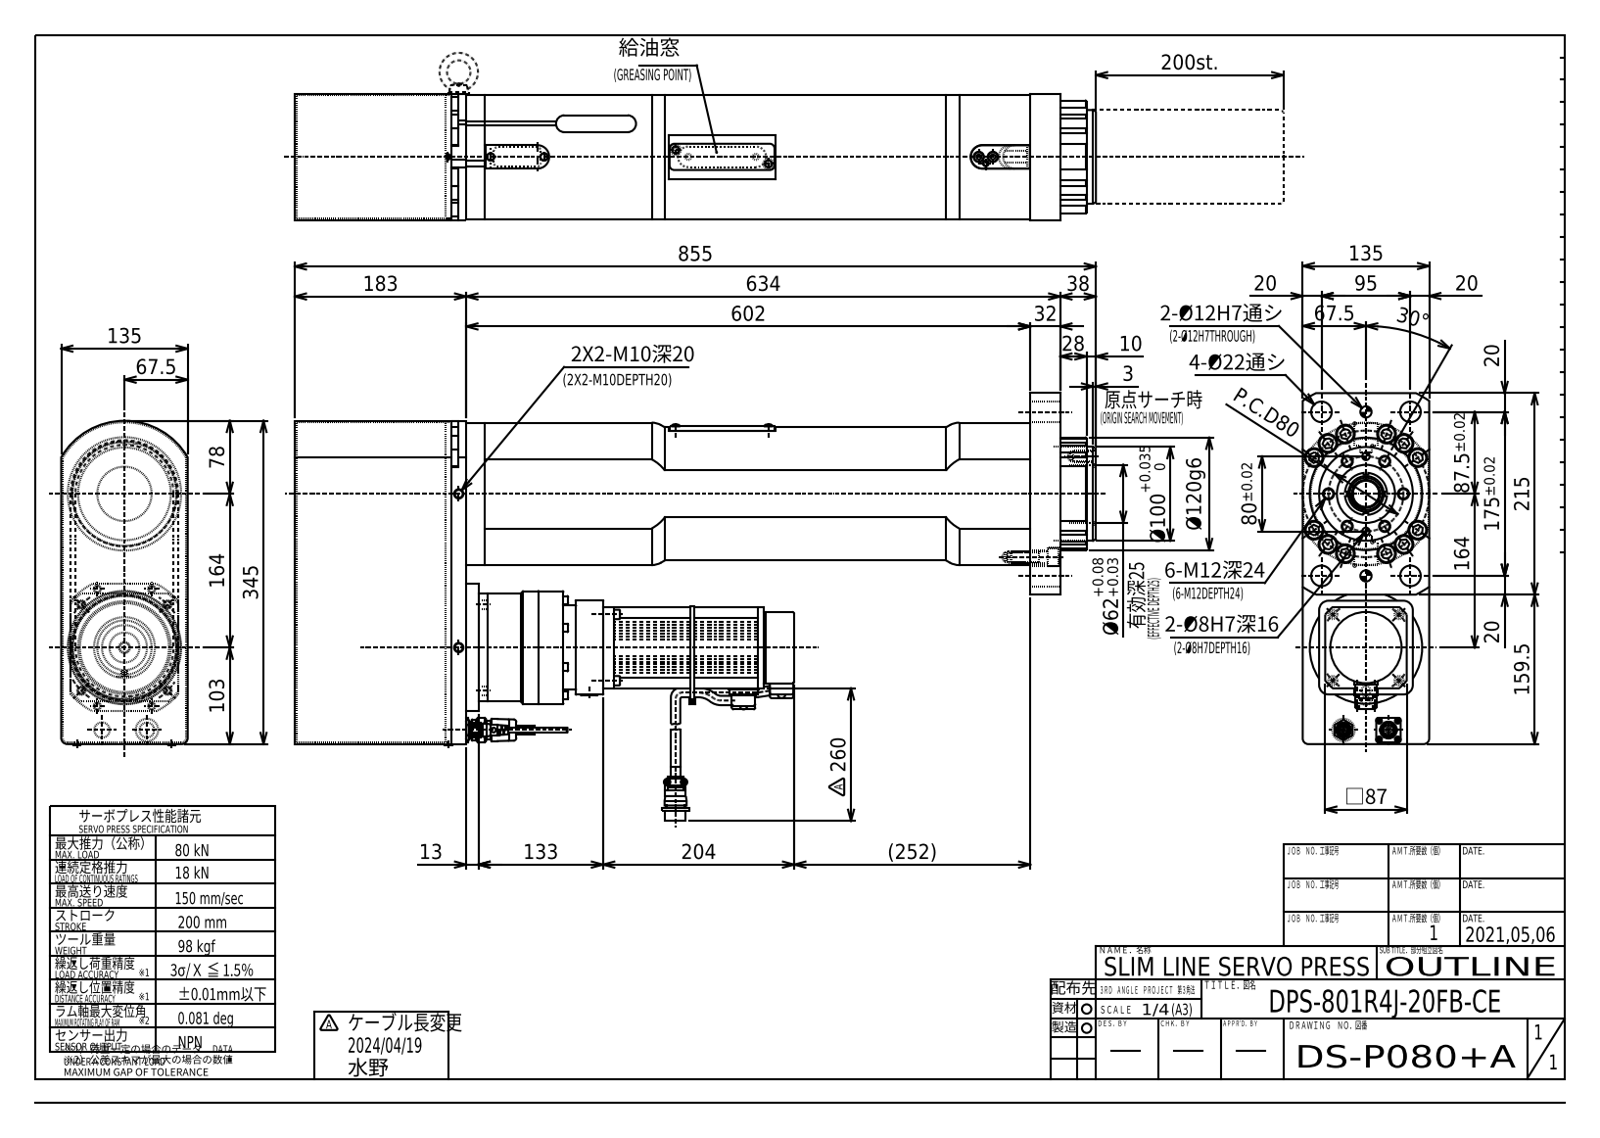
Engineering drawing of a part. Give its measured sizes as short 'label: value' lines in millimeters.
name: DPS-801R4J-20FB-CE(DS-P080)
written by: Autodesk Inventor 2023 (AUTOMOTIVE_DESIGN)
unit: mm
bodies: 2 solids, 1709 faces (877 planar, 438 cylindrical, 394 other)
size: 855 × 374.5 × 135
volume: 22 010 000 mm³; area: 889 208 mm²
holes: 8× ⌀4.92, 8× ⌀6.65, 7× ⌀1.1, 7× ⌀3.24, 6× ⌀10.11, 4× ⌀1.2, 4× ⌀4.5, 4× ⌀6.5, 4× ⌀8, 4× ⌀9, 4× ⌀22, 2× ⌀2.46
bosses: 7× ⌀18, 7× ⌀1.55, 7× ⌀1, 6× ⌀8, 4× ⌀8.5, 4× ⌀7.5, 4× ⌀7, 4× ⌀1.4
rounds: 48× R0.6, 29× R1, 17× R5, 16× R2, 13× R3, 11× R10, 9× R2.5, 9× R4
face distances: 135, 817, 32, 24, 111, 87, 3, 634, 183, 1.5
hole spacings: 40, 82.01, 47.5, 69.28, 10.26, 14.99, 20.71, 56.52
